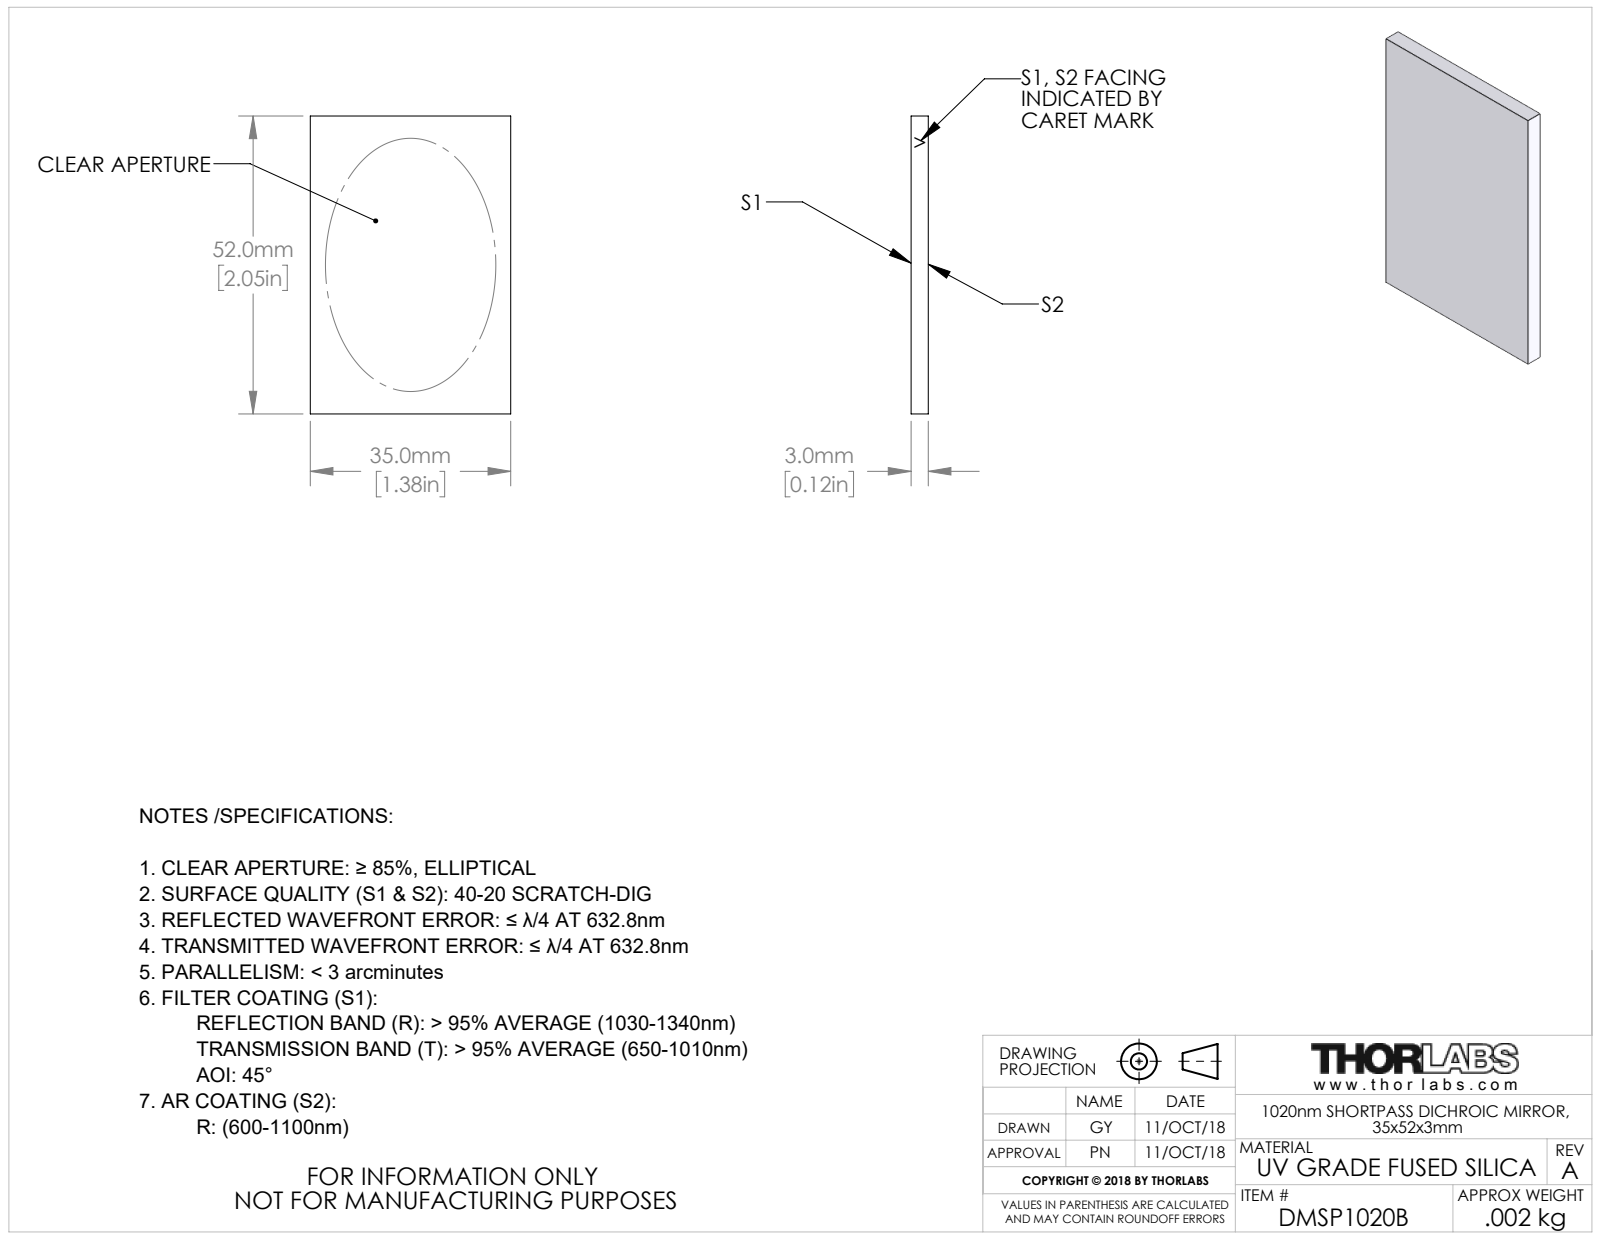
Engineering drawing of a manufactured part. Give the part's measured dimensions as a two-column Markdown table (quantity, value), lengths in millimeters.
| quantity | value |
| --- | --- |
| part name | TTN166721-E0W |
| STEP written by | SolidWorks 2018 (AUTOMOTIVE_DESIGN) |
| units | millimeters |
| bodies | 1 solid, 6 faces (6 planar, 0 cylindrical, 0 other) |
| overall size | 52 × 35 × 3 |
| volume | 5 460 mm³ |
| surface area | 4 162 mm² |
| main face-to-face distances | 3, 35, 52 |
